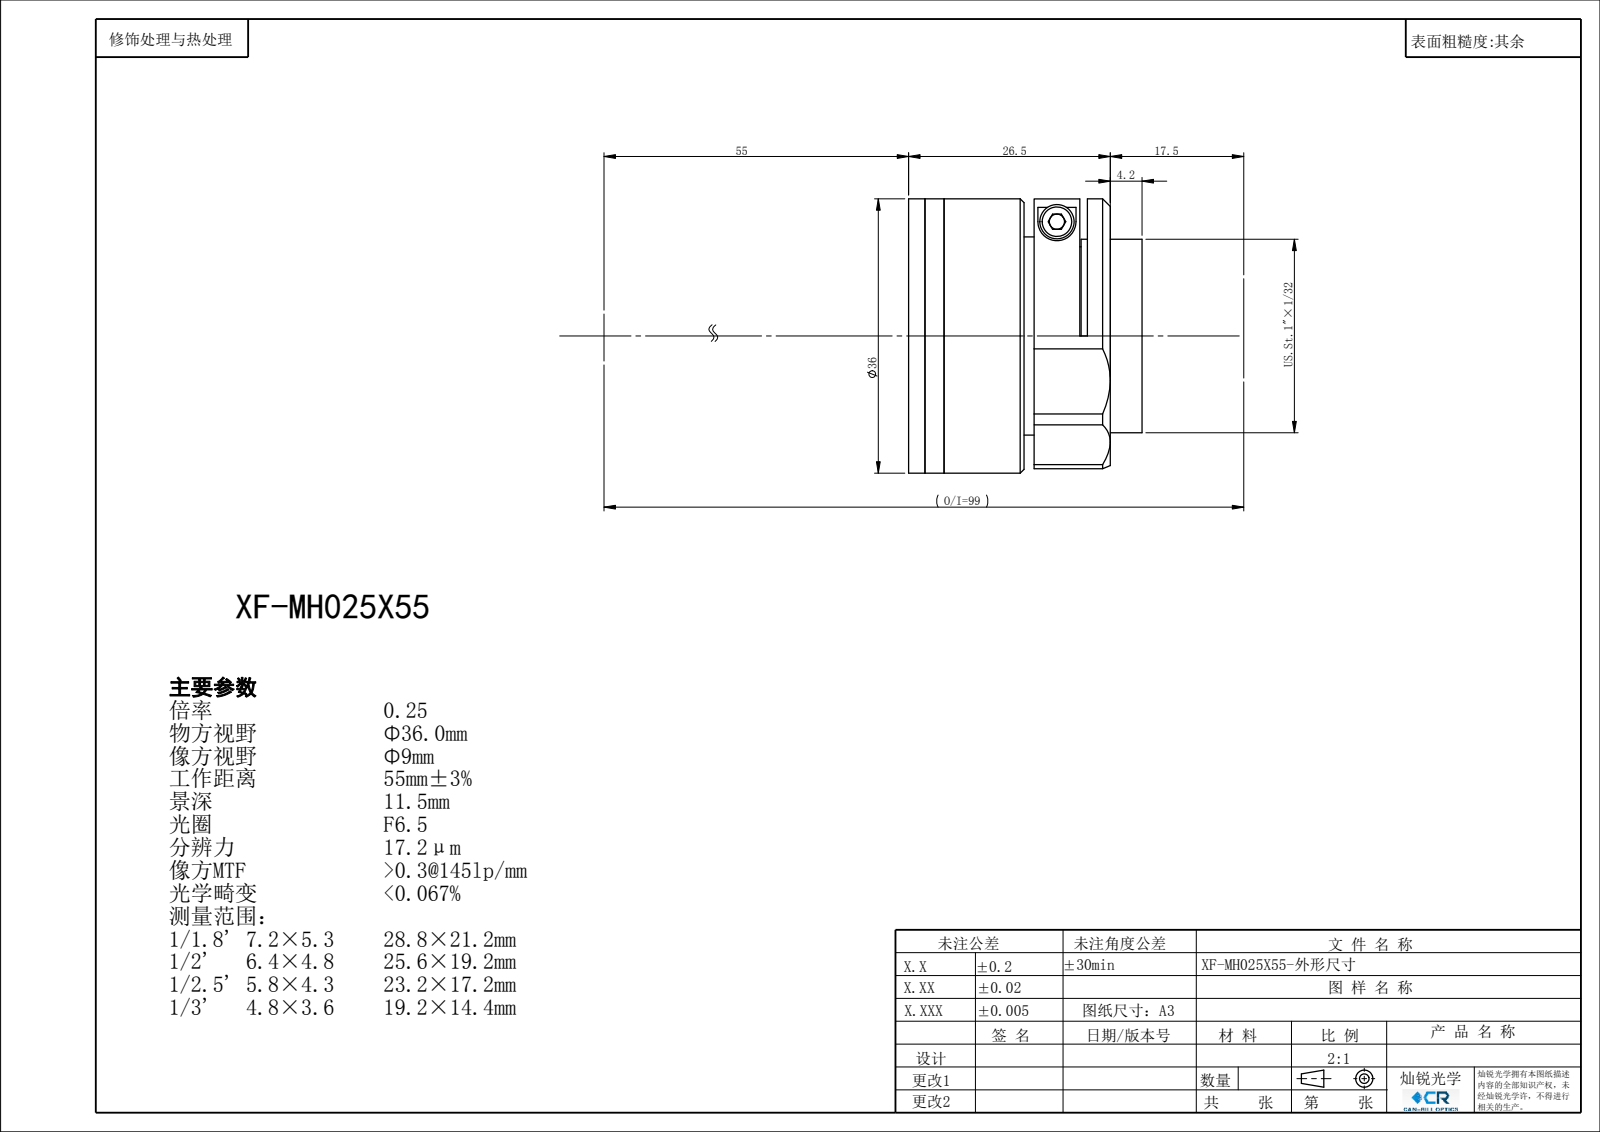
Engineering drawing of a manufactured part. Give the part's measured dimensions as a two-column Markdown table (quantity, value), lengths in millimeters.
| quantity | value |
| --- | --- |
| part name | XF-MH025X55 |
| STEP written by | SolidWorks 2022 (CONFIG_CONTROL_DESIGN) |
| units | millimeters |
| bodies | 0 solids, 107 faces (49 planar, 48 cylindrical, 10 other) |
| overall size | 36 × 36 × 30.48 |
| round holes (diameter × count) | 2.5 × 3, 7 × 1, 8.4 × 1, 10 × 1, 12 × 1, 14 × 1, 16 × 1, 18 × 1, 20 × 1, 21.5 × 1, 22 × 1, 24 × 1 |
| round bosses / shafts (diameter × count) | 36 × 1, 34 × 1, 25.4 × 1 |
| main face-to-face distances | 2.5, 4.65, 24.33, 21.83, 2.15, 26.48, 2, 1, 1.5, 24.98 |
